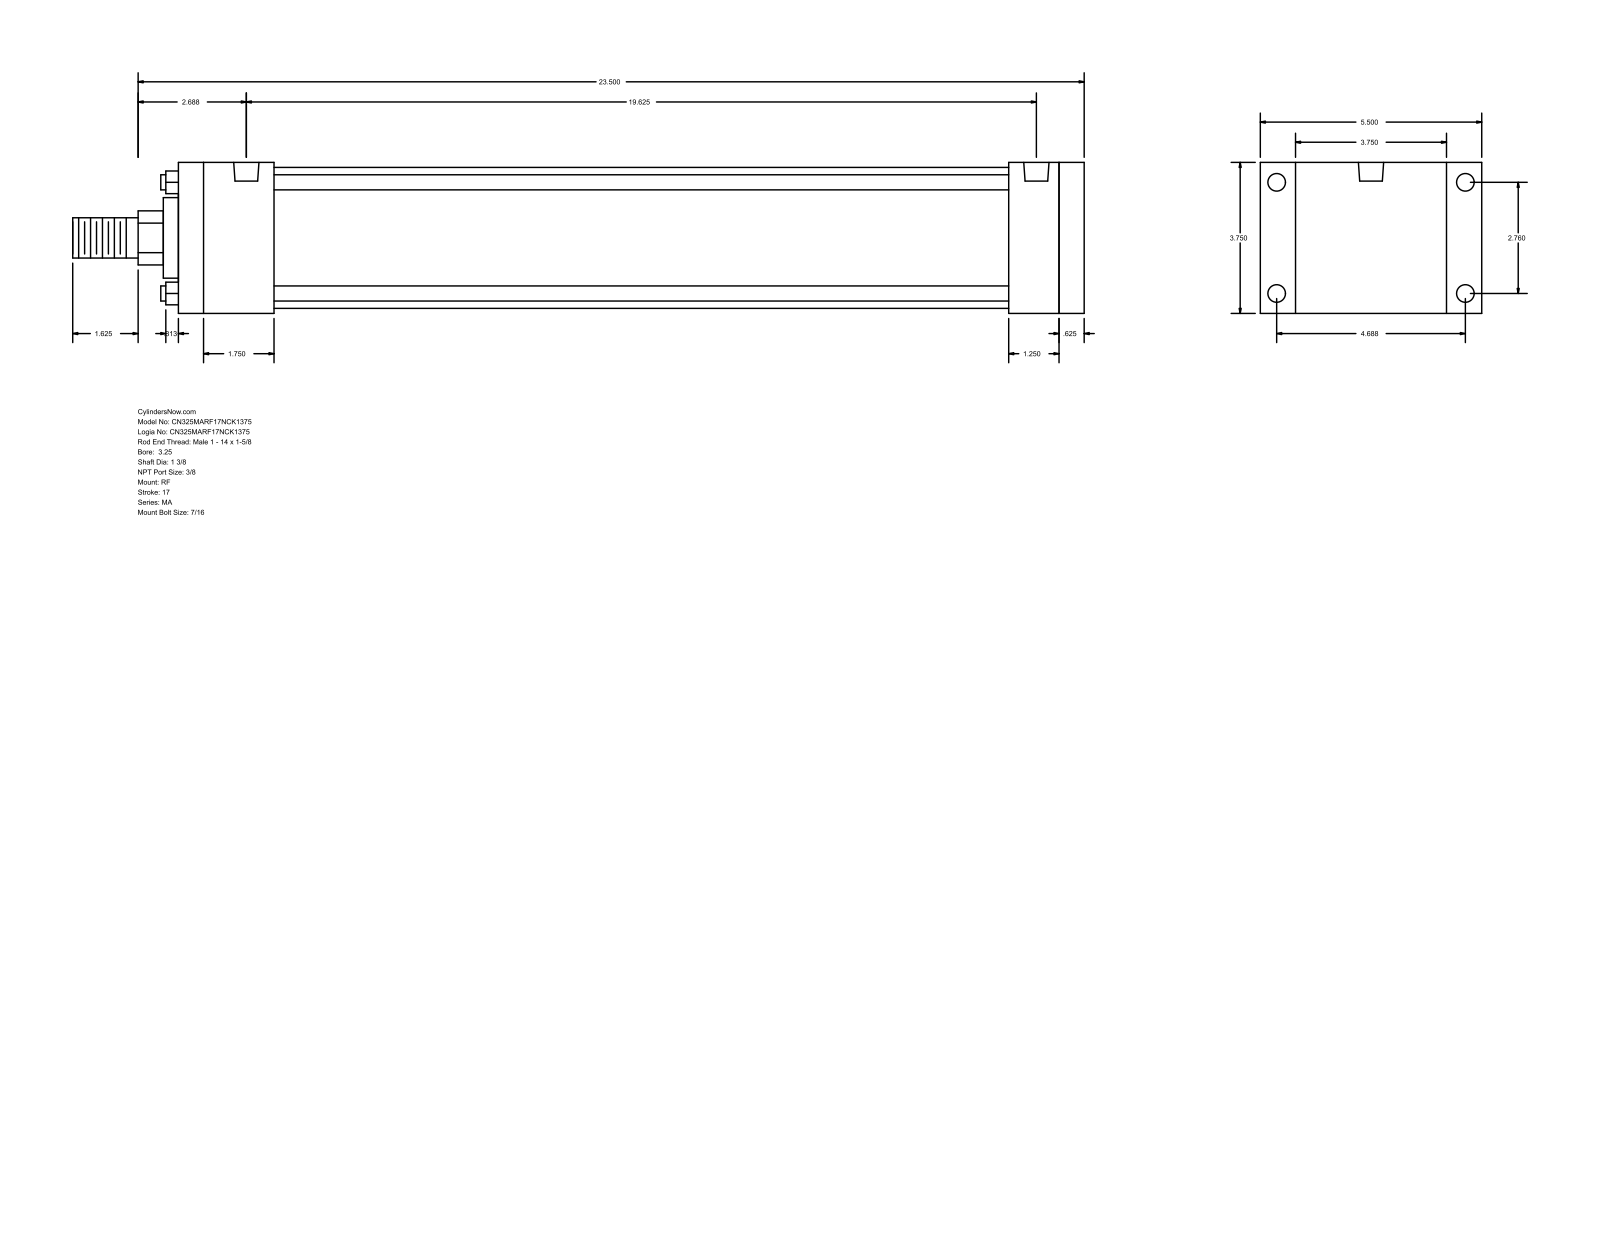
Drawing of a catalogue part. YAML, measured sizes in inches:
part_name: "MA_RF__0325_1.375"
step_written_by: "GSSL Pune (CONFIG_CONTROL_DESIGN)"
units: inches
bodies: {solids: 0, faces: 92, planar: 64, cylindrical: 28, other: 0}
overall_size: [25.125, 5.5, 3.75]
round_holes:
  - {diameter: 0.437, count: 8}
  - {diameter: 0.627, count: 2}
round_bosses_or_shafts:
  - {diameter: 0.375, count: 4}
  - {diameter: 3.5, count: 1}
  - {diameter: 2, count: 1}
  - {diameter: 1.375, count: 1}
  - {diameter: 1, count: 1}
partial_cylinders:
  - {radius: 0.672, count: 1}
face_to_face_distances: [3.75, 22.5, 0.625, 21.875, 0.875, 4.625, 20.625, 1.25, 1.875, 2.375]
hole_center_spacings: [2.76, 4.687, 5.439, 19.25, 0.187, 0.188, 19.437, 19.438]
